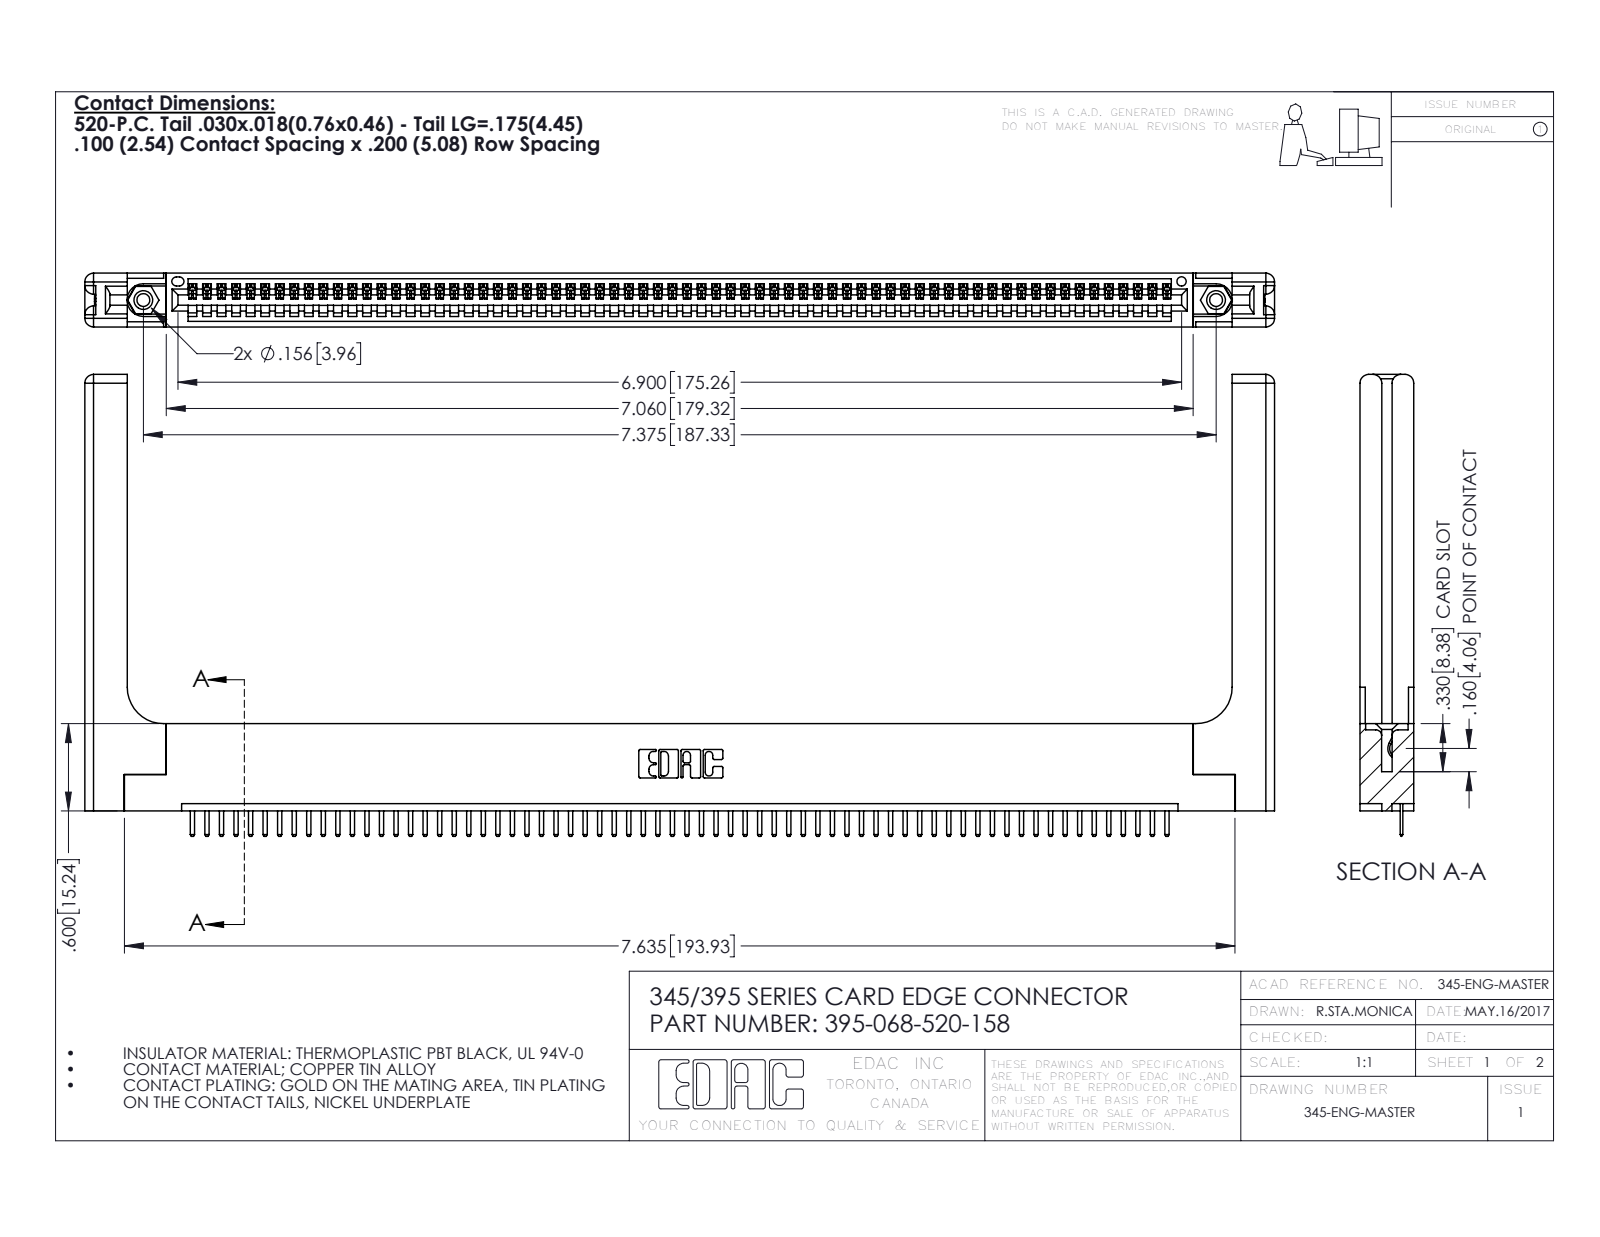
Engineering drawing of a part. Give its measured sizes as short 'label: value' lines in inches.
name: 395-068-520-158; 345-292-001_345-293-120; 345-250-001_345-250-001-102; 345-220-058_345-220-058 (+1 more)
written by: SolidWorks 2016 (CONFIG_CONTROL_DESIGN)
unit: in
bodies: 73 solids, 4598 faces (3084 planar, 1454 cylindrical, 60 other)
size: 8.179 × 3.175 × 0.37
volume: 1.724 in³; area: 48.46 in²
holes: 2× ⌀0.089, 2× ⌀0.125, 2× ⌀0.156, 1× ⌀0.064
bosses: 2× ⌀0.155
rounds: 138× R0.01, 136× R0.006, 22× R0.01, 16× R0.06, 6× R0.007, 6× R0.031, 3× R0.026, 2× R0.03
face distances: 0.072, 0.37, 0.298, 0.2, 0.098, 0.272, 0.025, 0.225, 0.148, 0.15
hole spacings: 0.27, 7.139, 7.375
